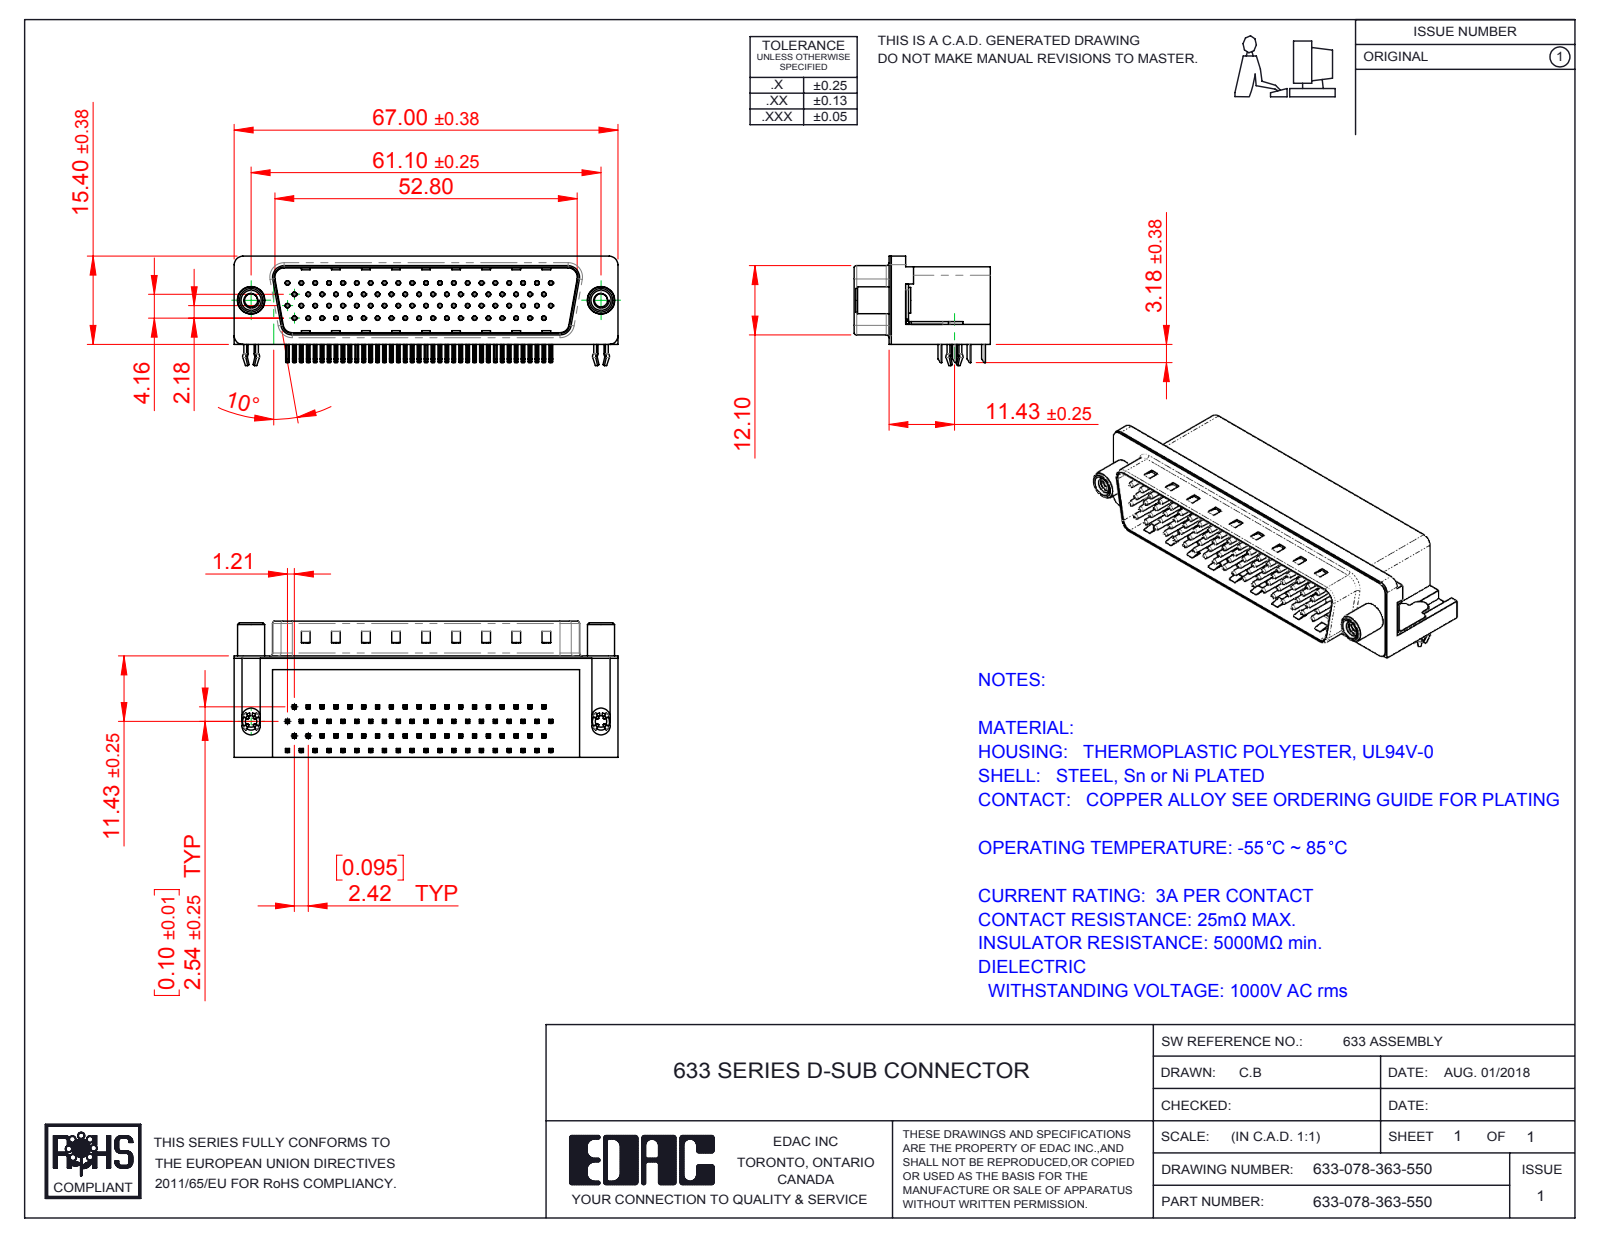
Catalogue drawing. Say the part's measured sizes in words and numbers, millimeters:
The part is named "633-078-363-550; 633 Contact Top 78; 633 4 Prong Board Lock_78 Contact; 633 Round Threaded Standoff (+5 more)". Its 3-D file was written by "SolidWorks 2016 (CONFIG_CONTROL_DESIGN)". It is 84 solids with 6390 faces: 4015 planar, 1792 cylindrical and 583 other. Overall it measures 67 by 23.8 by 19.1 millimeters. Its volume is 14 713 cubic millimeters and its surface area 16 628 square millimeters. Round holes: 78 of diameter 0.35, 78 of diameter 0.8, 2 of diameter 2, 2 of diameter 2.3, 2 of diameter 3.1, 2 of diameter 4, 2 of diameter 4.8, 2 of diameter 5. Round bosses or shafts: 78 of diameter 0.75, 2 of diameter 4.9, 2 of diameter 4.7, 2 of diameter 4.5, 2 of diameter 3.85, 2 of diameter 3. Partial cylindrical surfaces (rounded edges, fillets, slot ends): 316 of radius 0.25, 156 of radius 0.12, 16 of radius 1, 9 of radius 0.5, 8 of radius 1.6, 6 of radius 1.5, 4 of radius 0.45, 4 of radius 0.9. The main face-to-face distances are 0.4, 13.2, 17.3, 11.7, 13.35, 2.05, 13.75, 1.65, 1.85, 11.9. The hole center spacings are 2.42, 4.84, 7.26, 9.68, 6.26, 7.13, 12.1, 8.62.
